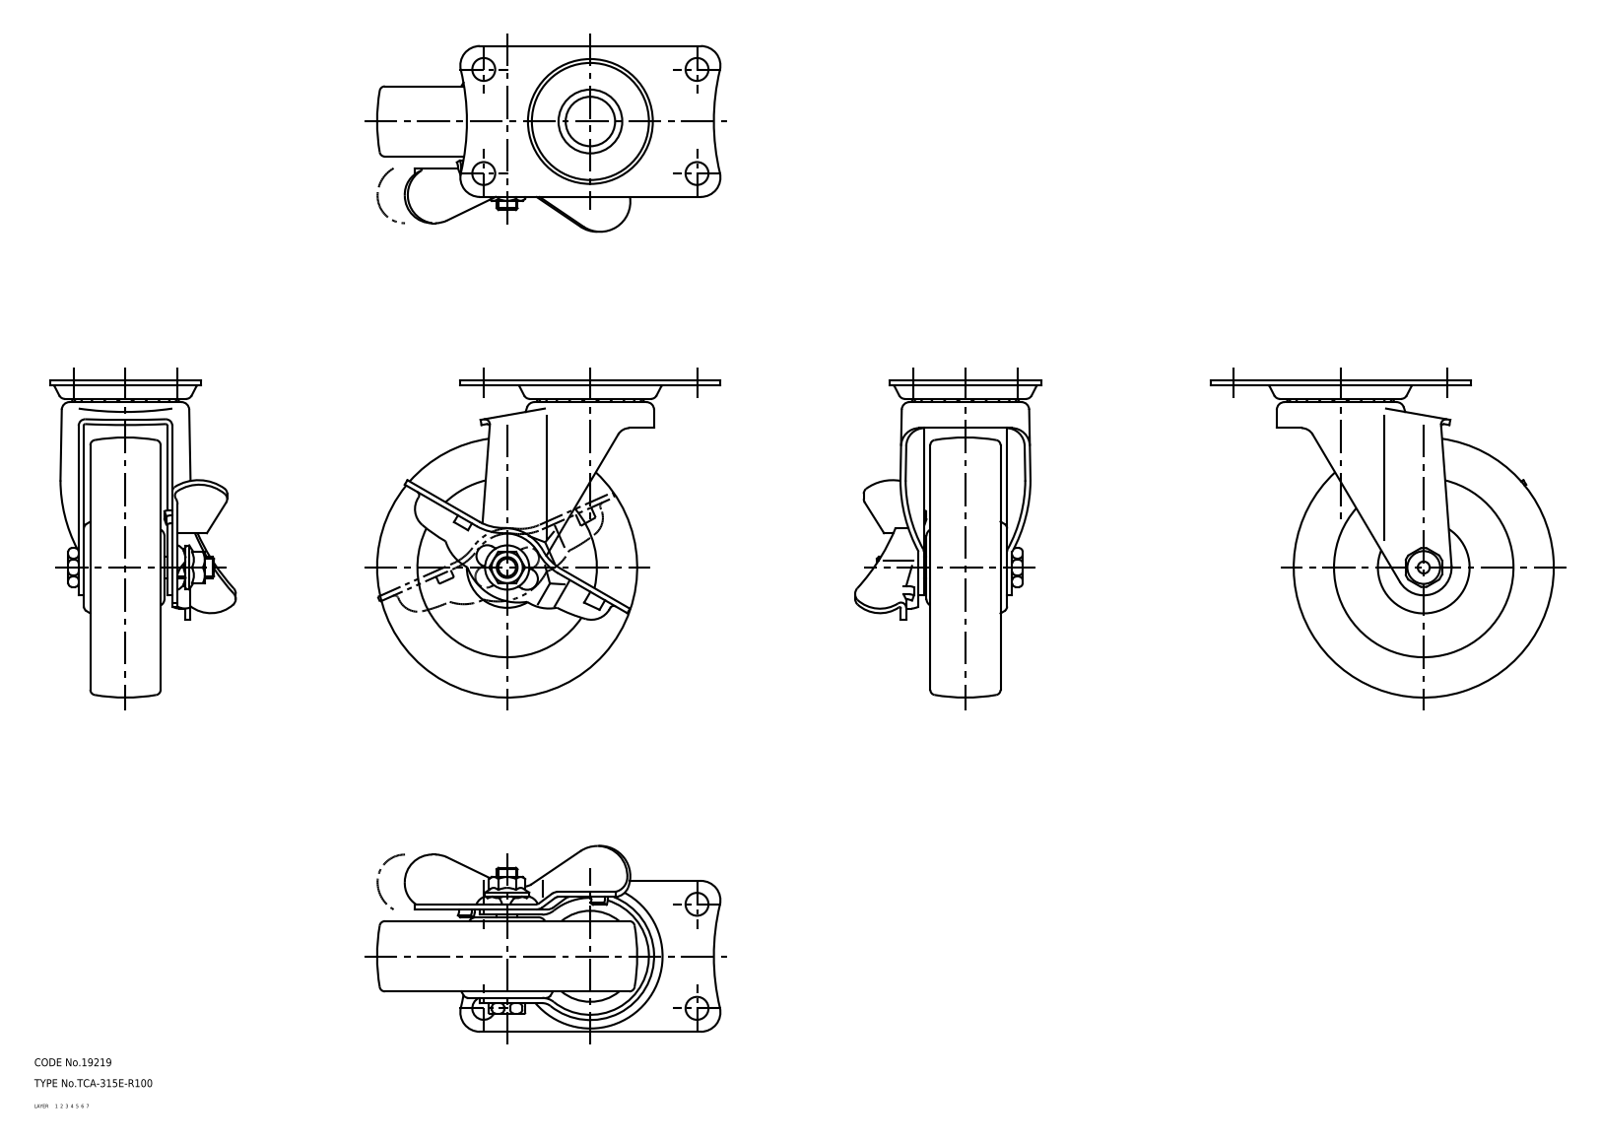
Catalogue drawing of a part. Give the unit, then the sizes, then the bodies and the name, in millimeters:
Units: millimetres
Overall size (bounding box): 132 × 122 × 71.4
Volume: 250 848 mm³ · Surface area: 66 285 mm²
Bodies: 6 solids, 405 faces (0 planar, 0 cylindrical, 405 other)
Part name (STEP PRODUCT): lever; wheel; mounting plate; main shaft (+2 more)
STEP written by: CADfix (AUTOMOTIVE_DESIGN)
